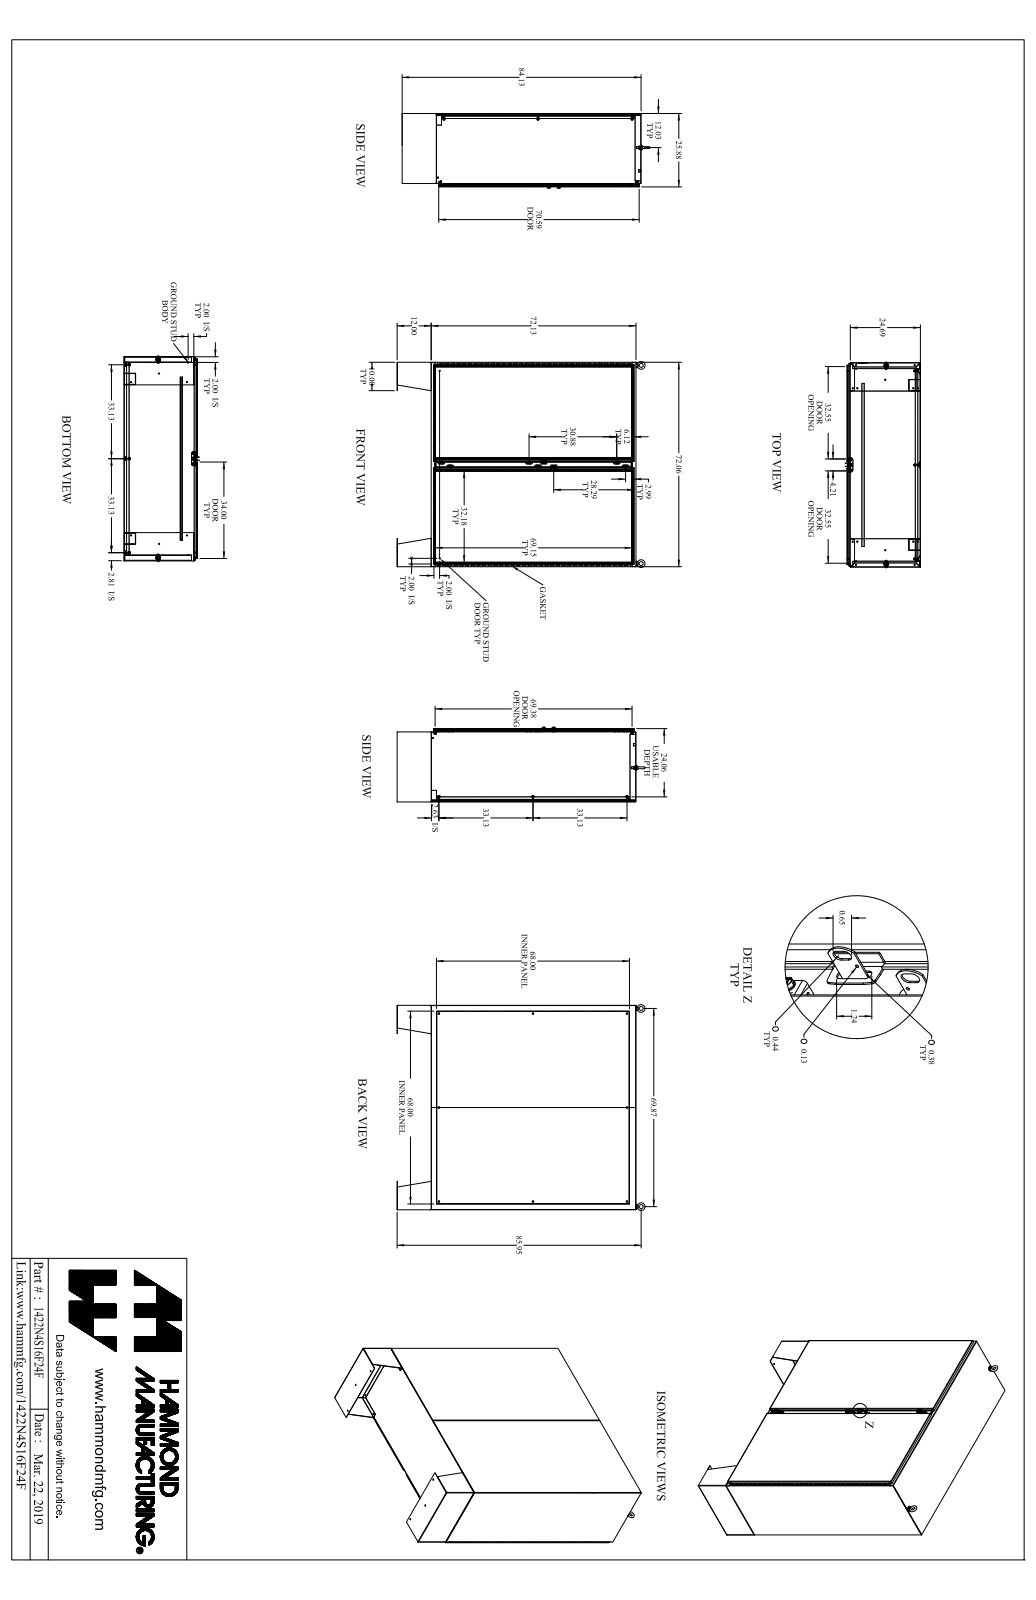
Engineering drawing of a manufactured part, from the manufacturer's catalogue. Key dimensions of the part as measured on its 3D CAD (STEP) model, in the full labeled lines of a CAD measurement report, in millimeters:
Part name (STEP PRODUCT): 1422N4S16F24F_Default
STEP written by: SolidWorks 2019 (CONFIG_CONTROL_DESIGN)
Units: millimetres
Bodies: 110 solids, 3522 faces (1696 planar, 1582 cylindrical, 244 other)
Overall size (bounding box): 2229.7 × 1857.3 × 671.5
Volume: 43 880 000 mm³ · Surface area: 35 030 000 mm²
Round holes (diameter × count): ⌀7.7 ×24, ⌀11.1 ×14, ⌀7.8 ×8, ⌀11.3 ×8, ⌀14.3 ×8, ⌀5.4 ×6, ⌀6.7 ×6, ⌀9.5 ×6, ⌀5.1 ×3, ⌀6.4 ×3, ⌀8 ×3, ⌀2.8 ×2
Round bosses / shafts (diameter × count): ⌀25.4 ×8, ⌀16.5 ×8, ⌀9.5 ×8, ⌀8.4 ×8, ⌀12.7 ×6, ⌀9.9 ×6, ⌀6.2 ×6, ⌀8 ×4
Partial cylindrical surfaces — rounded edges, fillets, slot ends (radius × count): R1.2 ×69, R3.6 ×69, R6.4 ×34, R1.5 ×18, R2.9 ×12, R3.6 ×12, R3.2 ×10, R4.7 ×10
Main face-to-face distances: 2.4, 654.8, 652.4, 3.2, 657.2, 609.5, 612, 42.8, 45.3, 615.1
Hole centre spacings: 152.4, 1789.2, 304.8, 1808.5, 457.2, 609.6, 1884, 762
